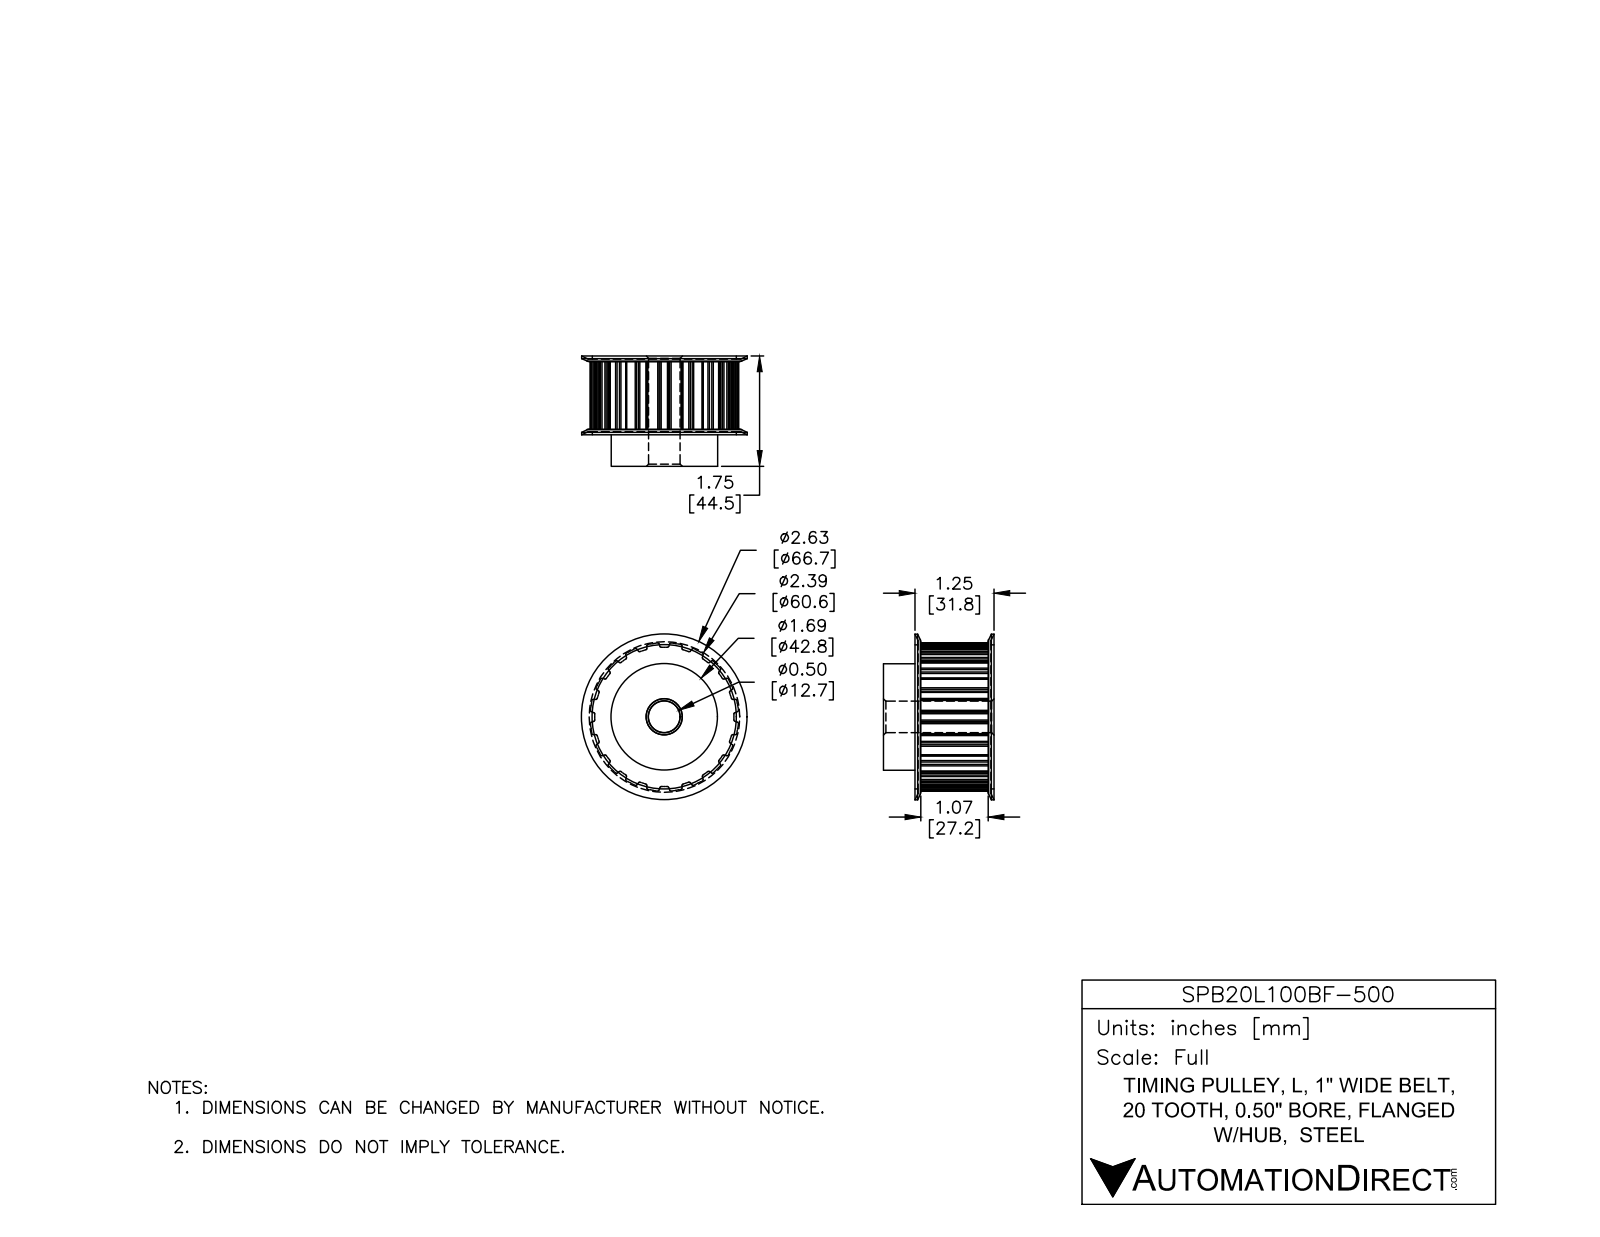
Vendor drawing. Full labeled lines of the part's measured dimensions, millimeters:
Part name (STEP PRODUCT): SPB20L100BF-500
STEP written by: SolidWorks 2015 (AUTOMOTIVE_DESIGN)
Units: millimetres
Bodies: 1 solid, 209 faces (67 planar, 126 cylindrical, 16 other)
Overall size (bounding box): 66.7 × 66.7 × 44.5
Volume: 98 930 mm³ · Surface area: 19 200 mm²
Round holes (diameter × count): ⌀12.7 ×1
Round bosses / shafts (diameter × count): ⌀66.7 ×1, ⌀66.7 ×1, ⌀58 ×1, ⌀42.8 ×1
Partial cylindrical surfaces — rounded edges, fillets, slot ends (radius × count): R0.5 ×80, R29.9 ×1
Main face-to-face distances: 44.5, 31.8, 12.7, 56.1, 1.3, 30.5, 2.3, 29.5, 1, 28.2
